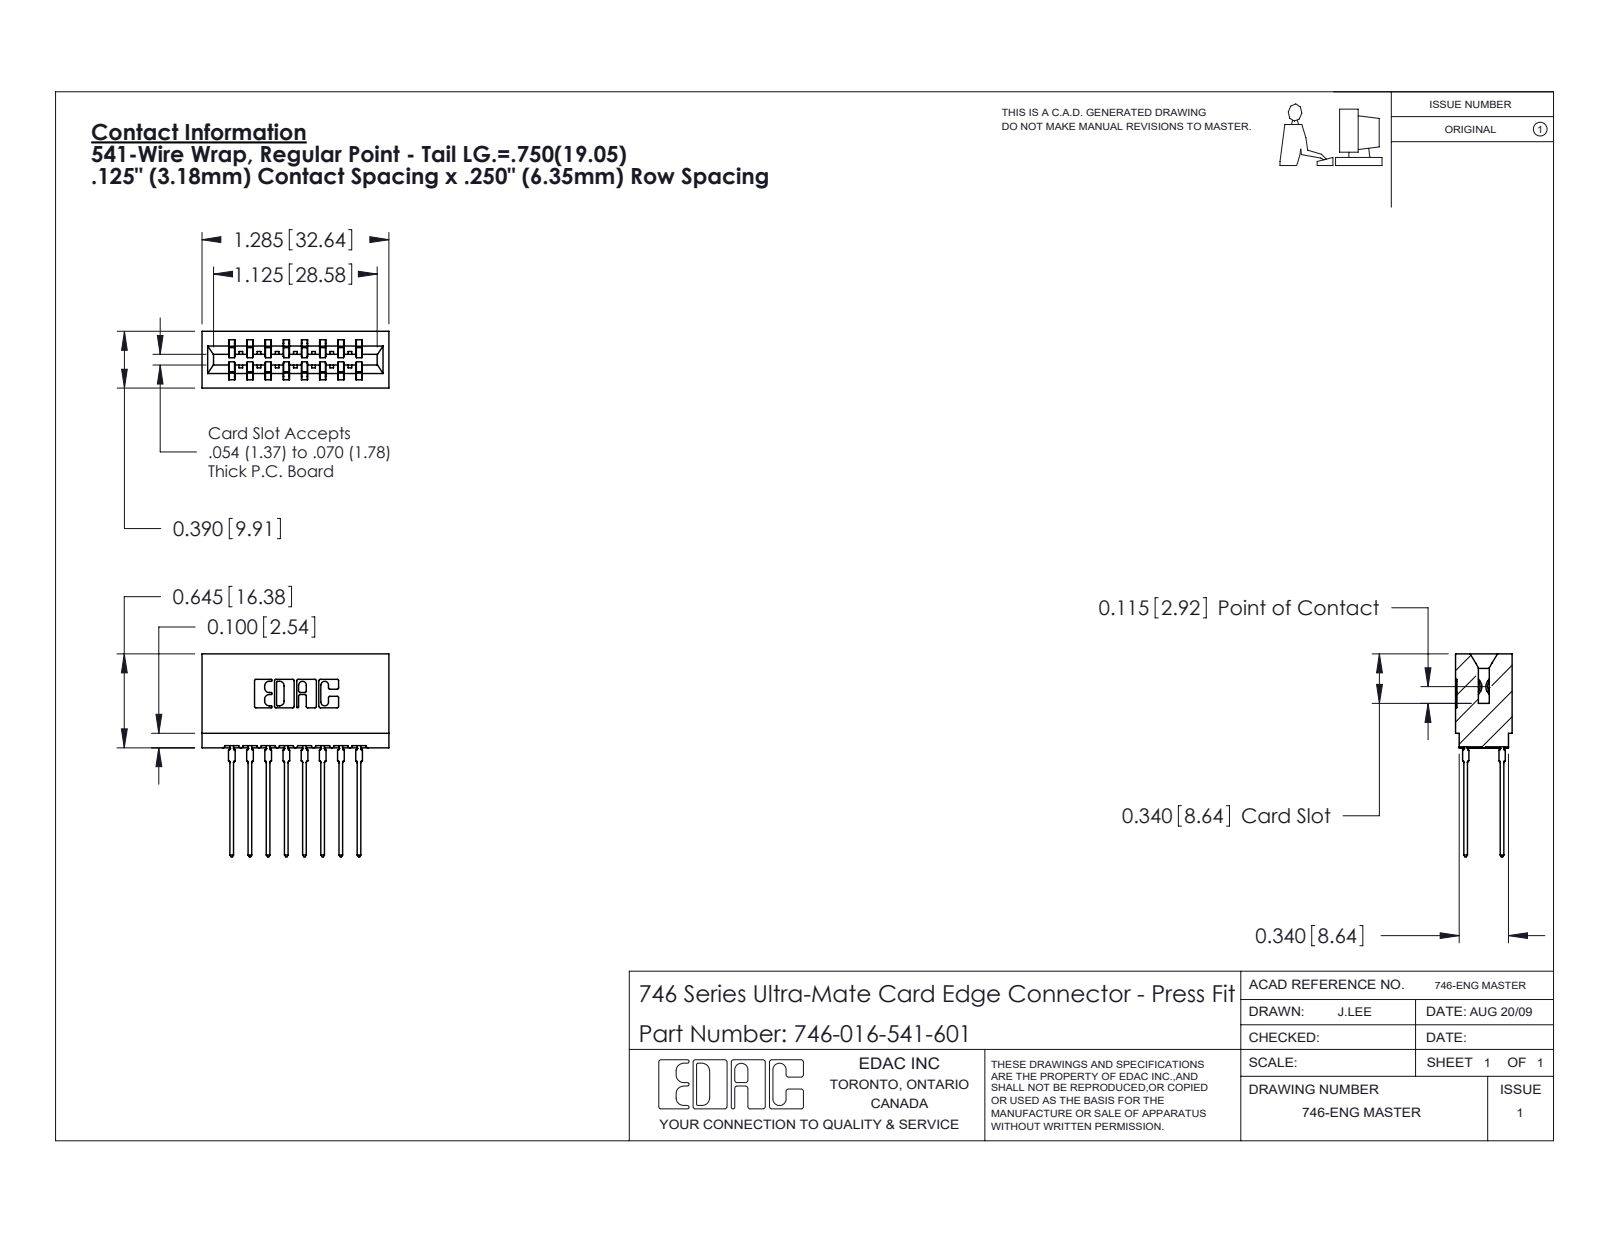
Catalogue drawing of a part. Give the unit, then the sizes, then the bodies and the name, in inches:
Units: inches
Overall size (bounding box): 1.394 × 1.285 × 0.39
Partial cylindrical surfaces — rounded edges, fillets, slot ends (radius × count): R0.021 ×32, R0.01 ×22, R0.015 ×9, R0.005 ×8, R0.011 ×8, R0.007 ×6, R0.031 ×6, R0.026 ×3
Main face-to-face distances: 0.25, 0.333, 0.057, 0.042, 0.125, 0.5, 0.083, 0.292, 0.375, 0.208
Volume: 0.246 in³ · Surface area: 8.857 in²
Bodies: 17 solids, 1529 faces (791 planar, 322 cylindrical, 416 other)
Part name (STEP PRODUCT): 746 Part_.340 Slot Depth - 01; 746-292-001_541; 746-016-541-601
STEP written by: SolidWorks 2020 (CONFIG_CONTROL_DESIGN)
